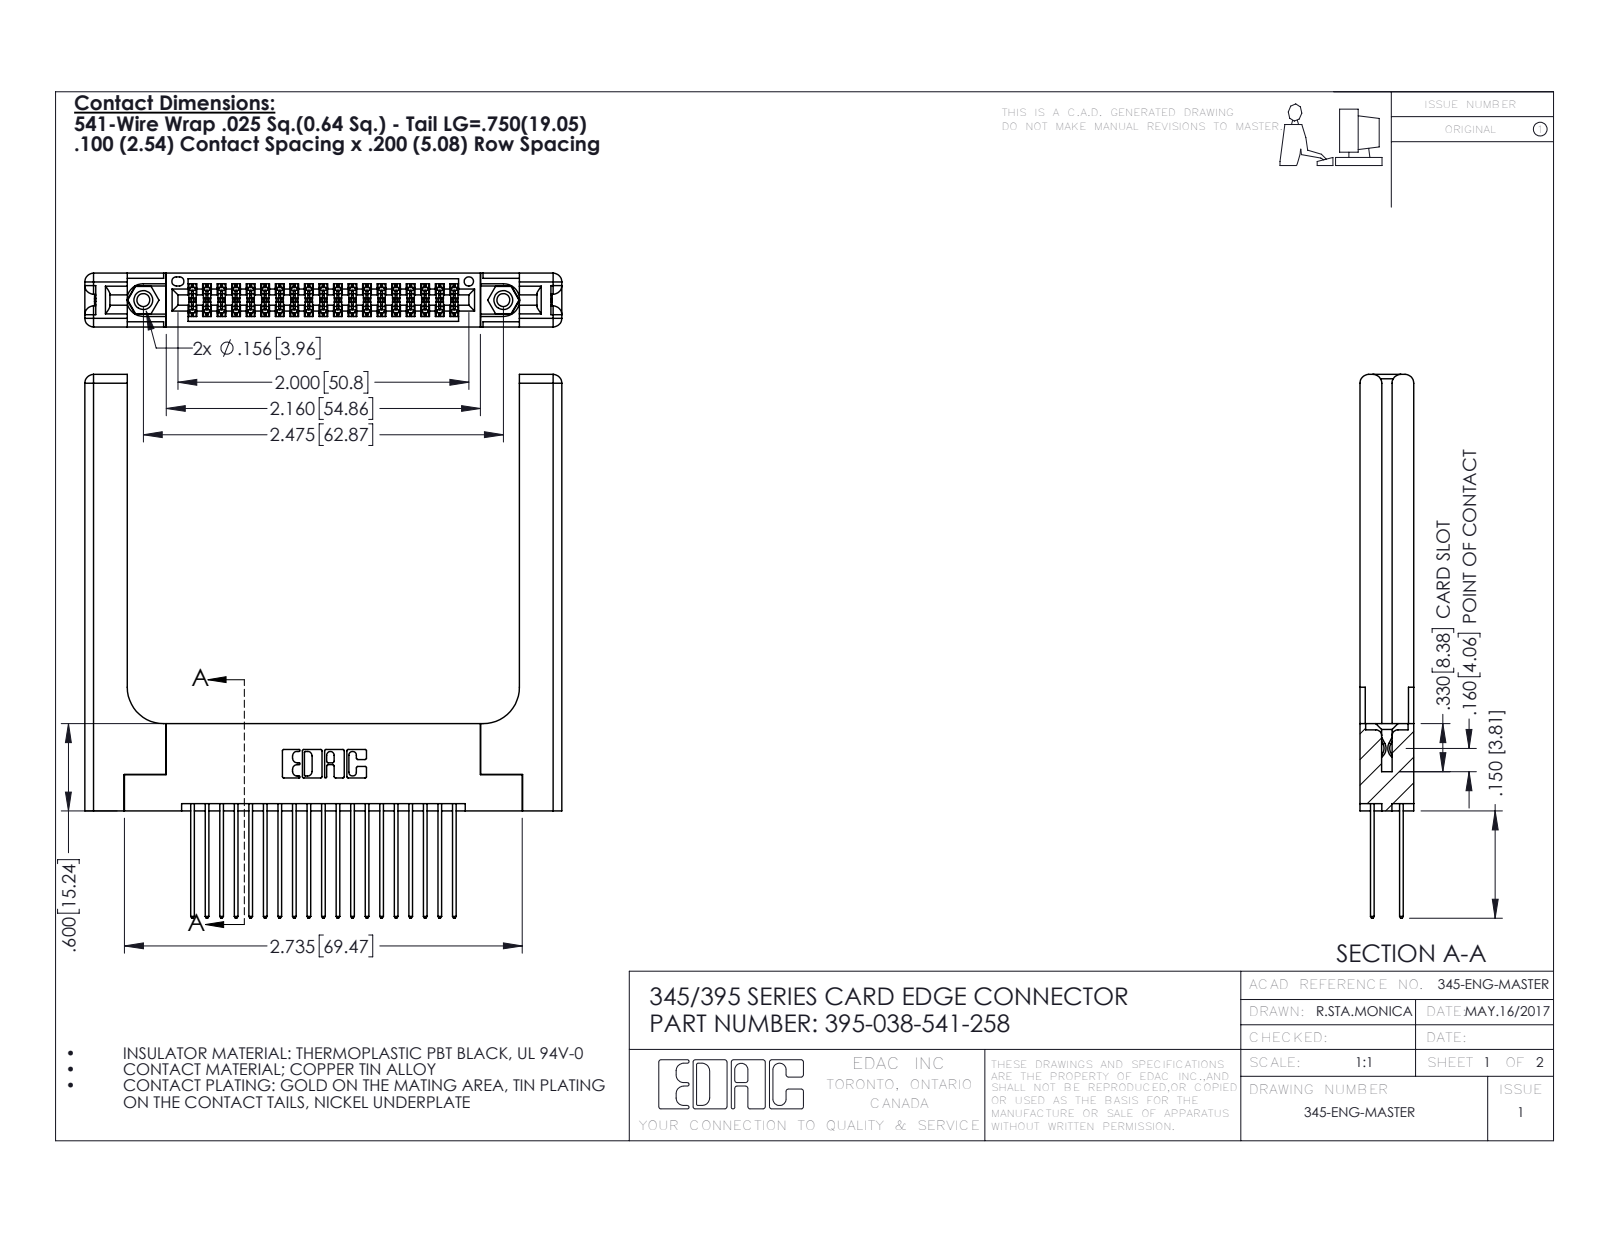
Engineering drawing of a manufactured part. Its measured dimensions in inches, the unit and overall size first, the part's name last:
Units: inches
Overall size (bounding box): 3.737 × 3.279 × 0.37
Round holes (diameter × count): ⌀0.089 ×2, ⌀0.125 ×2, ⌀0.156 ×2, ⌀0.064 ×1
Round bosses / shafts (diameter × count): ⌀0.155 ×2
Partial cylindrical surfaces — rounded edges, fillets, slot ends (radius × count): R0.006 ×57, R0.01 ×38, R0.01 ×22, R0.06 ×16, R0.007 ×6, R0.031 ×6, R0.026 ×3, R0.014 ×2
Main face-to-face distances: 0.072, 0.37, 0.298, 0.2, 0.098, 0.272, 0.025, 0.225, 0.15, 0.148
Hole centre spacings: 0.27, 2.241, 2.475
Volume: 1.011 in³ · Surface area: 27.29 in²
Bodies: 43 solids, 2282 faces (1482 planar, 740 cylindrical, 60 other)
Part name (STEP PRODUCT): 395-038-541-258; 345-250-001_345-250-001-102; 345-220-058_345-220-058; 345 Part_Flush Mounting Lugs - 0.156 Dia-TH (+1 more)
STEP written by: SolidWorks 2016 (CONFIG_CONTROL_DESIGN)
